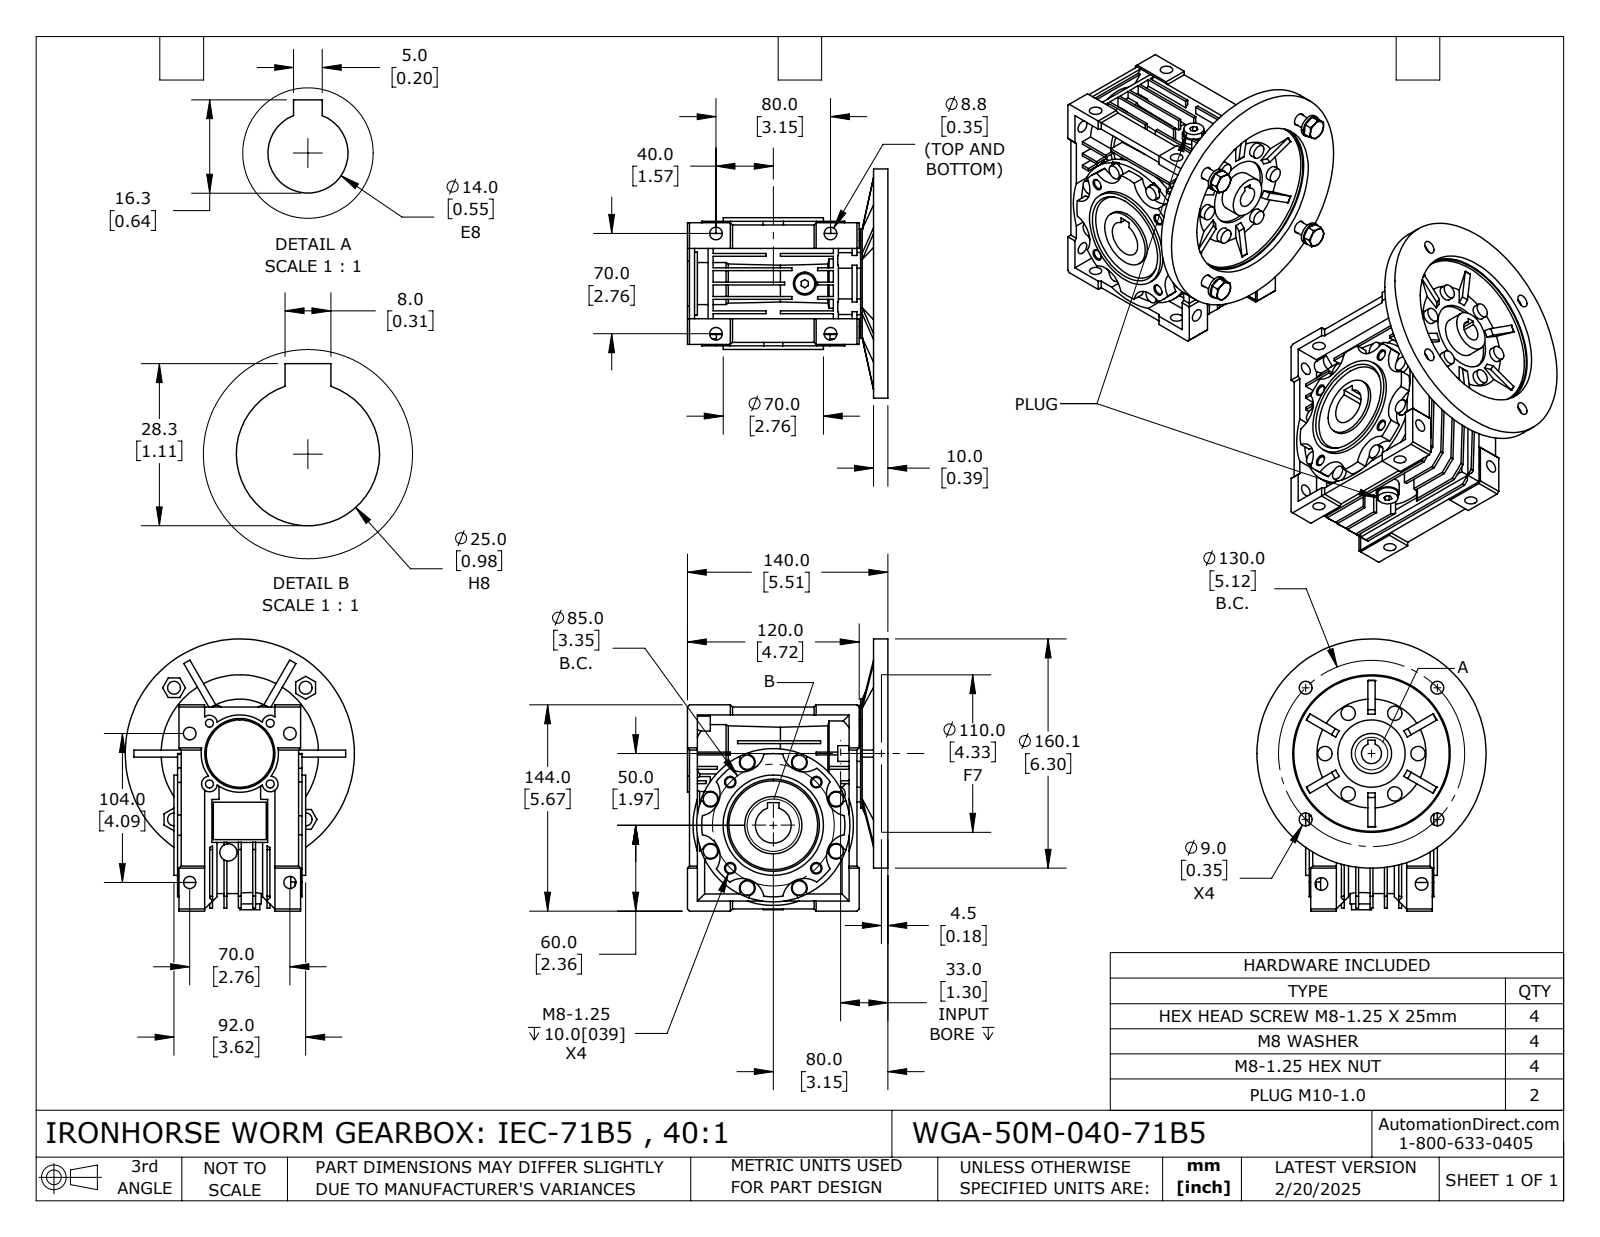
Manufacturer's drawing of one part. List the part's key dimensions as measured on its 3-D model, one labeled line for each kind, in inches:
Part name (STEP PRODUCT): WGA-50M-040-71B5
STEP written by: SolidWorks 2024 (CONFIG_CONTROL_DESIGN)
Units: inches
Bodies: 7 solids, 1007 faces (577 planar, 316 cylindrical, 114 other)
Overall size (bounding box): 7.481 × 6.302 × 5.512
Volume: 69.93 in³ · Surface area: 397.8 in²
Round holes (diameter × count): ⌀0.346 ×8, ⌀0.335 ×6, ⌀0.354 ×6, ⌀0.219 ×4, ⌀0.262 ×2, ⌀0.262 ×2, ⌀0.551 ×1, ⌀0.591 ×1, ⌀0.984 ×1, ⌀1.102 ×1, ⌀1.339 ×1, ⌀1.575 ×1
Round bosses / shafts (diameter × count): ⌀0.394 ×14, ⌀0.63 ×2, ⌀0.551 ×2, ⌀0.386 ×2, ⌀0.327 ×2, ⌀6.302 ×1, ⌀4.213 ×1, ⌀2.992 ×1
Partial cylindrical surfaces — rounded edges, fillets, slot ends (radius × count): R0.217 ×18, R0.236 ×8, R0.591 ×8, R0.61 ×8, R0.817 ×1, R1.811 ×1, R1.878 ×1, R1.969 ×1
Main face-to-face distances: 0.394, 0.079, 0.276, 0.217, 0.315, 0.059, 0.787, 0.197, 2.165, 1.378
Hole centre spacings: 2.818, 2.756, 1.181, 1.378, 1.67, 1.673, 2.366, 2.559
